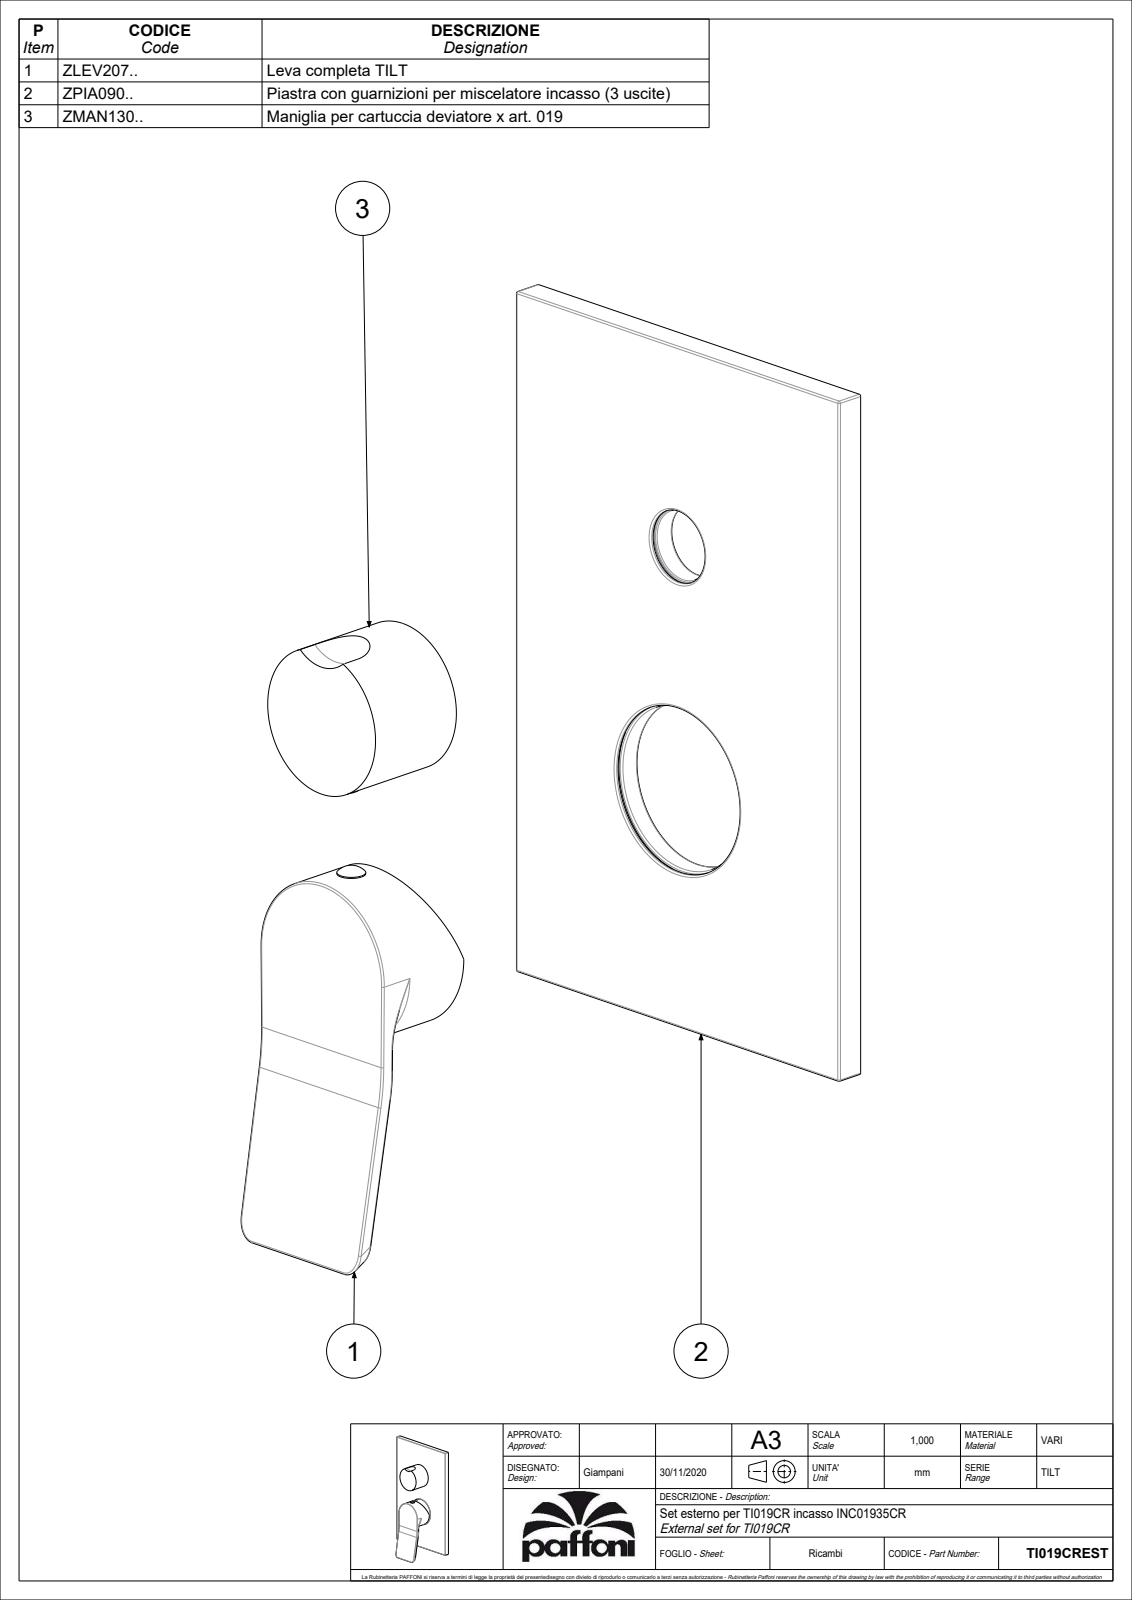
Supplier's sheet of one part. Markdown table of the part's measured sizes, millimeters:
| quantity | value |
| --- | --- |
| part name | TI018CREST |
| STEP written by | CREO PARAMETRIC BY PTC INC, 2020044 (CONFIG_CONTROL_DESIGN) |
| units | millimeters |
| bodies | 3 solids, 277 faces (100 planar, 99 cylindrical, 78 other) |
| overall size | 203.58 × 120 × 48.95 |
| volume | 163 899 mm³ |
| surface area | 103 113 mm² |
| round holes (diameter × count) | 3 × 2, 3.2 × 1, 4.2 × 1, 14.8 × 1, 19.2 × 1, 20 × 1, 21 × 1, 23.2 × 1, 36 × 1, 45 × 1, 46 × 1, 47 × 1 |
| round bosses / shafts (diameter × count) | 7.6 × 2, 5.5 × 2, 51 × 1, 49 × 1, 45.5 × 1, 40 × 1, 25 × 1, 24 × 1 |
| partial cylindrical surfaces (radius × count) | 0.5 × 18, 1 × 8, 1.5 × 2, 5 × 2, 12.5 × 1, 44.14 × 1, 63 × 1 |
| main face-to-face distances | 2.5, 8, 5.5, 0.5, 5, 3, 22.5, 4.01, 35, 40 |
| hole center spacings | 1, 10, 68, 78 |
